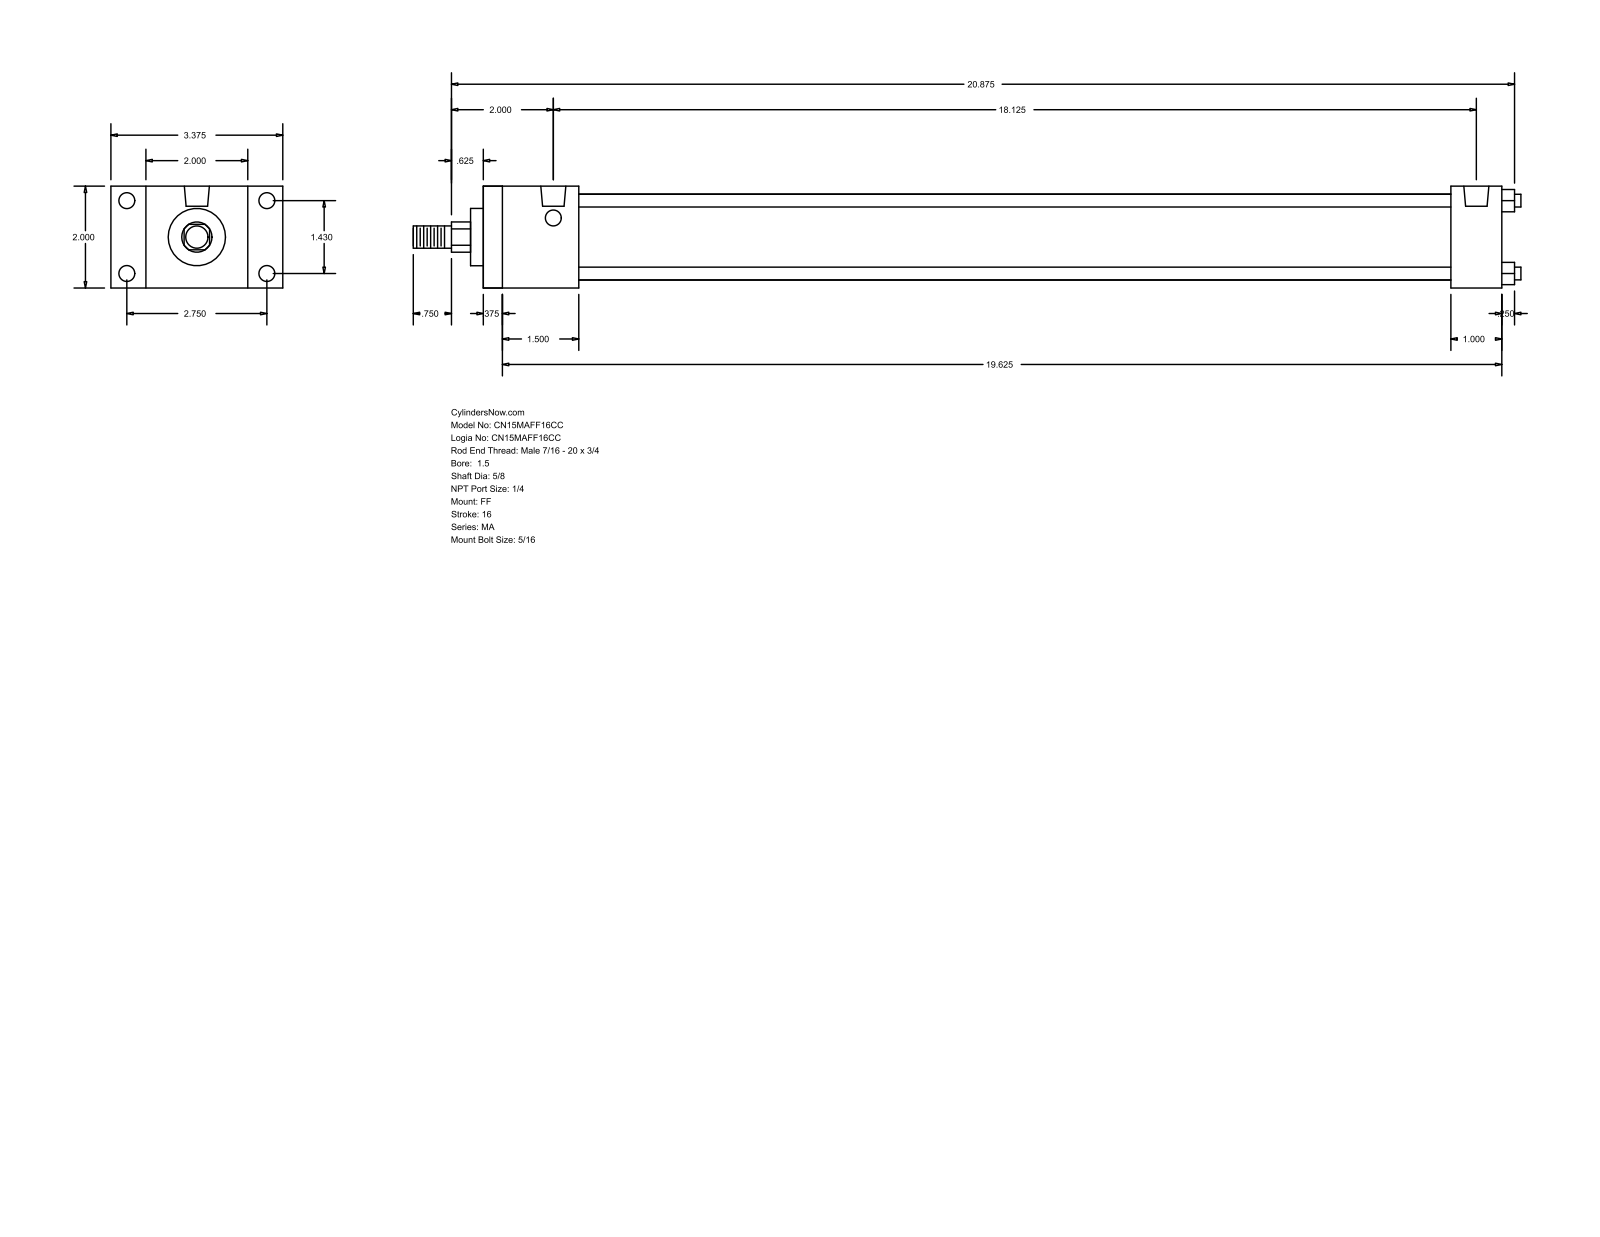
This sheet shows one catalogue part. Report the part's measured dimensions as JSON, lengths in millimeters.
{"part_name": "MA_FF__0150_0.625", "step_written_by": "GSSL Pune (CONFIG_CONTROL_DESIGN)", "units": "millimeters", "bodies": {"solids": 0, "faces": 92, "planar": 64, "cylindrical": 28, "other": 0}, "overall_size": [552.45, 85.72, 50.8], "round_holes": [[7.94, 8], [12.49, 2]], "round_bosses_or_shafts": [[6.35, 4], [42.93, 1], [28.57, 1], [15.88, 1], [11.11, 1]], "partial_cylinders_radius": [[7.54, 1]], "face_to_face_distances": [50.8, 508, 9.52, 498.48, 25.4, 47.62, 482.6, 38.1, 473.08, 434.98], "hole_center_spacings": [36.32, 69.84, 78.72, 460.38]}
